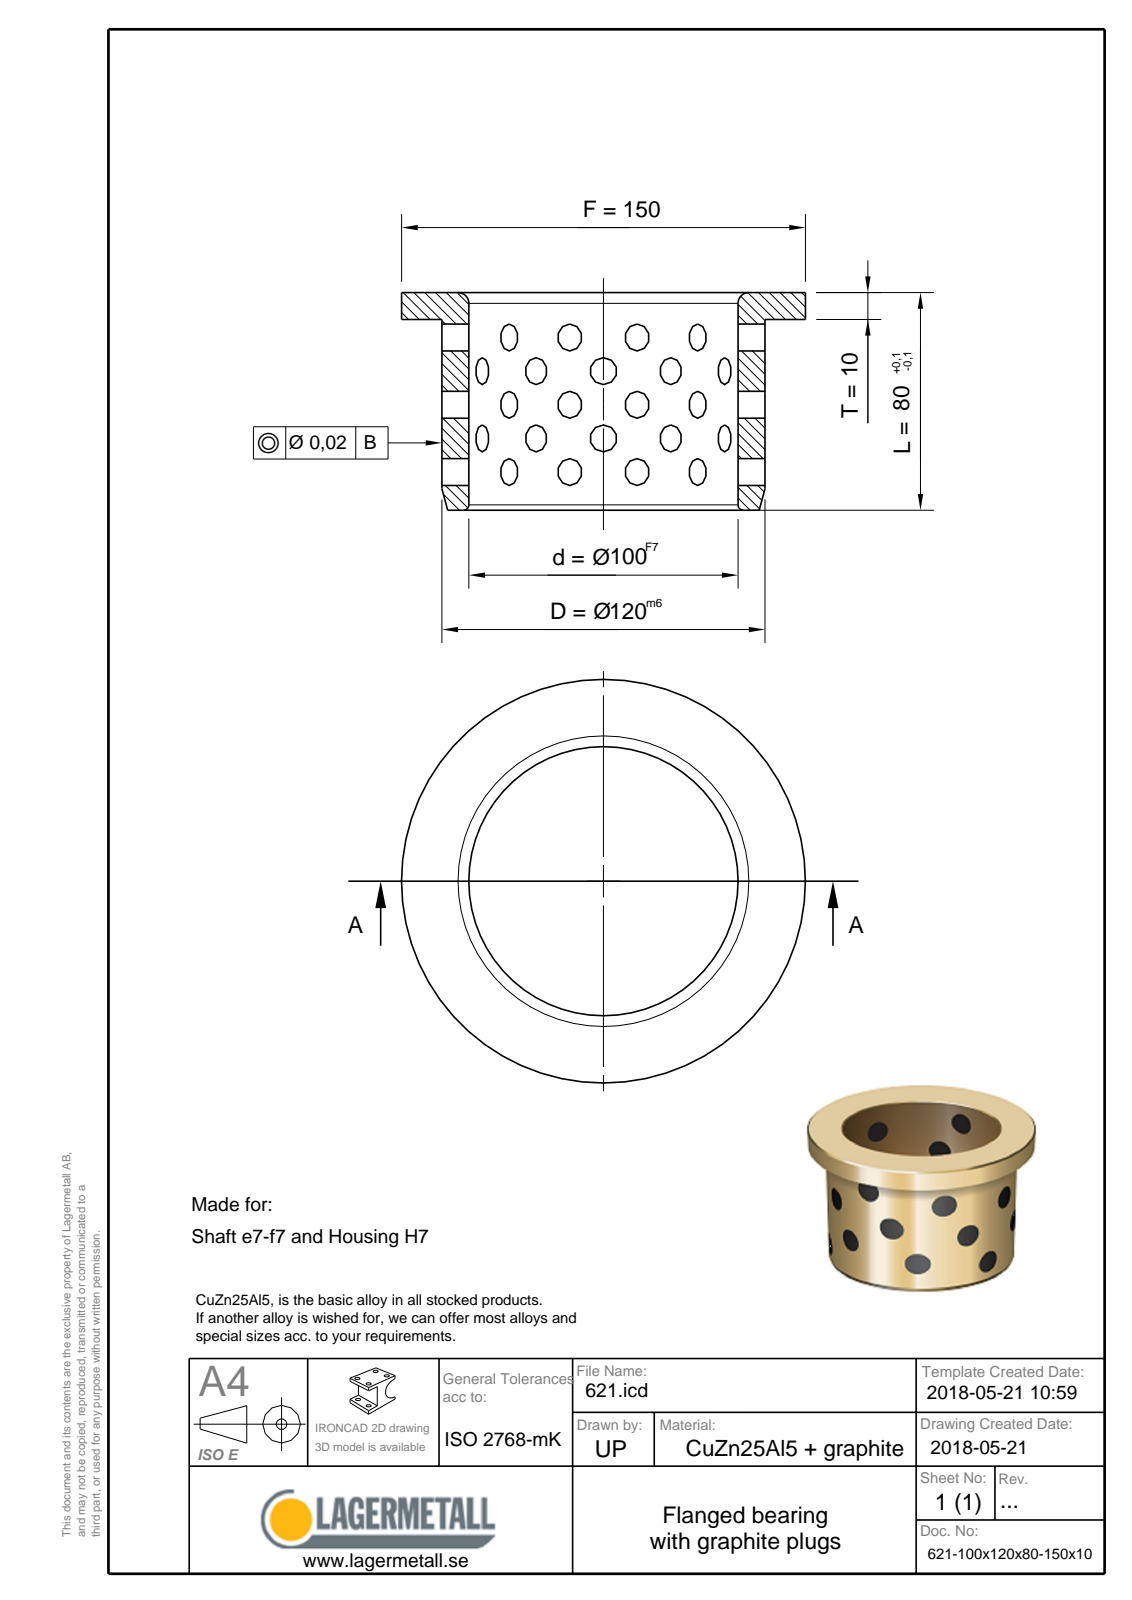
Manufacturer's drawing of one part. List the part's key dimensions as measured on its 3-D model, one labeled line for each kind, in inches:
Part name (STEP PRODUCT): 621-100x120x80-150x10
STEP written by: Spatial InterOp 3D (CONFIG_CONTROL_DESIGN)
Units: inches
Bodies: 1 solid, 9 faces (3 planar, 3 cylindrical, 3 other)
Overall size (bounding box): 5.906 × 5.906 × 3.15
Volume: 20.65 in³ · Surface area: 115.9 in²
Round holes (diameter × count): ⌀3.937 ×1
Round bosses / shafts (diameter × count): ⌀5.906 ×1, ⌀4.724 ×1
Main face-to-face distances: 0.394, 2.756, 3.15
